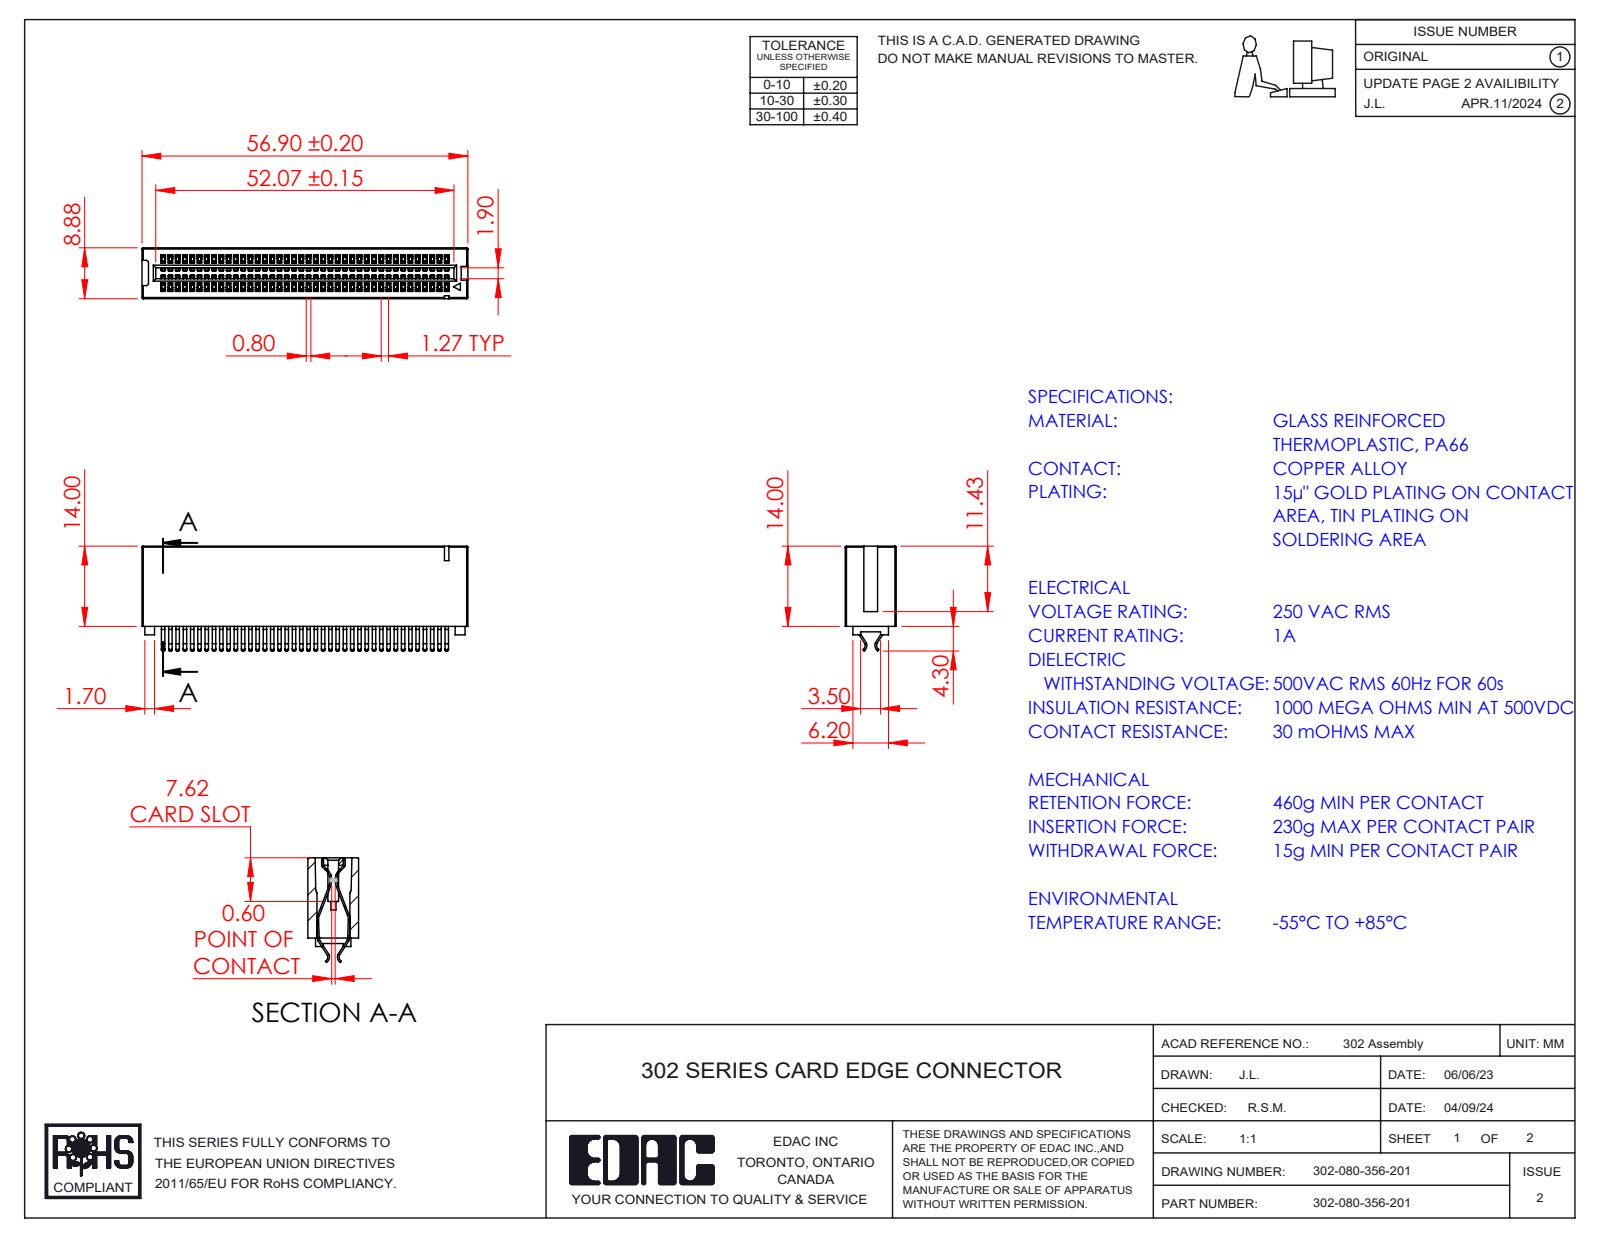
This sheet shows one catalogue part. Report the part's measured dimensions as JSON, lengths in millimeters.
{"part_name": "302-080-356-201; HSG_Vertical HSG; Contact_302-290-X56", "step_written_by": "SolidWorks 2023 (CONFIG_CONTROL_DESIGN)", "units": "millimeters", "bodies": {"solids": 81, "faces": 3866, "planar": 2569, "cylindrical": 1293, "other": 4}, "overall_size": [56.9, 18.3, 8.88], "volume_mm3": 4408, "surface_area_mm2": 12311, "partial_cylinders_radius": [[0.2, 248], [0.11, 2], [0.4, 2], [0.41, 2], [0.93, 2], [1.05, 2], [1.23, 2], [1.25, 2]], "face_to_face_distances": [1.27, 2.54, 3.81, 5.08, 7.62, 6.35, 8.88, 8.89, 10.16, 11.43]}
